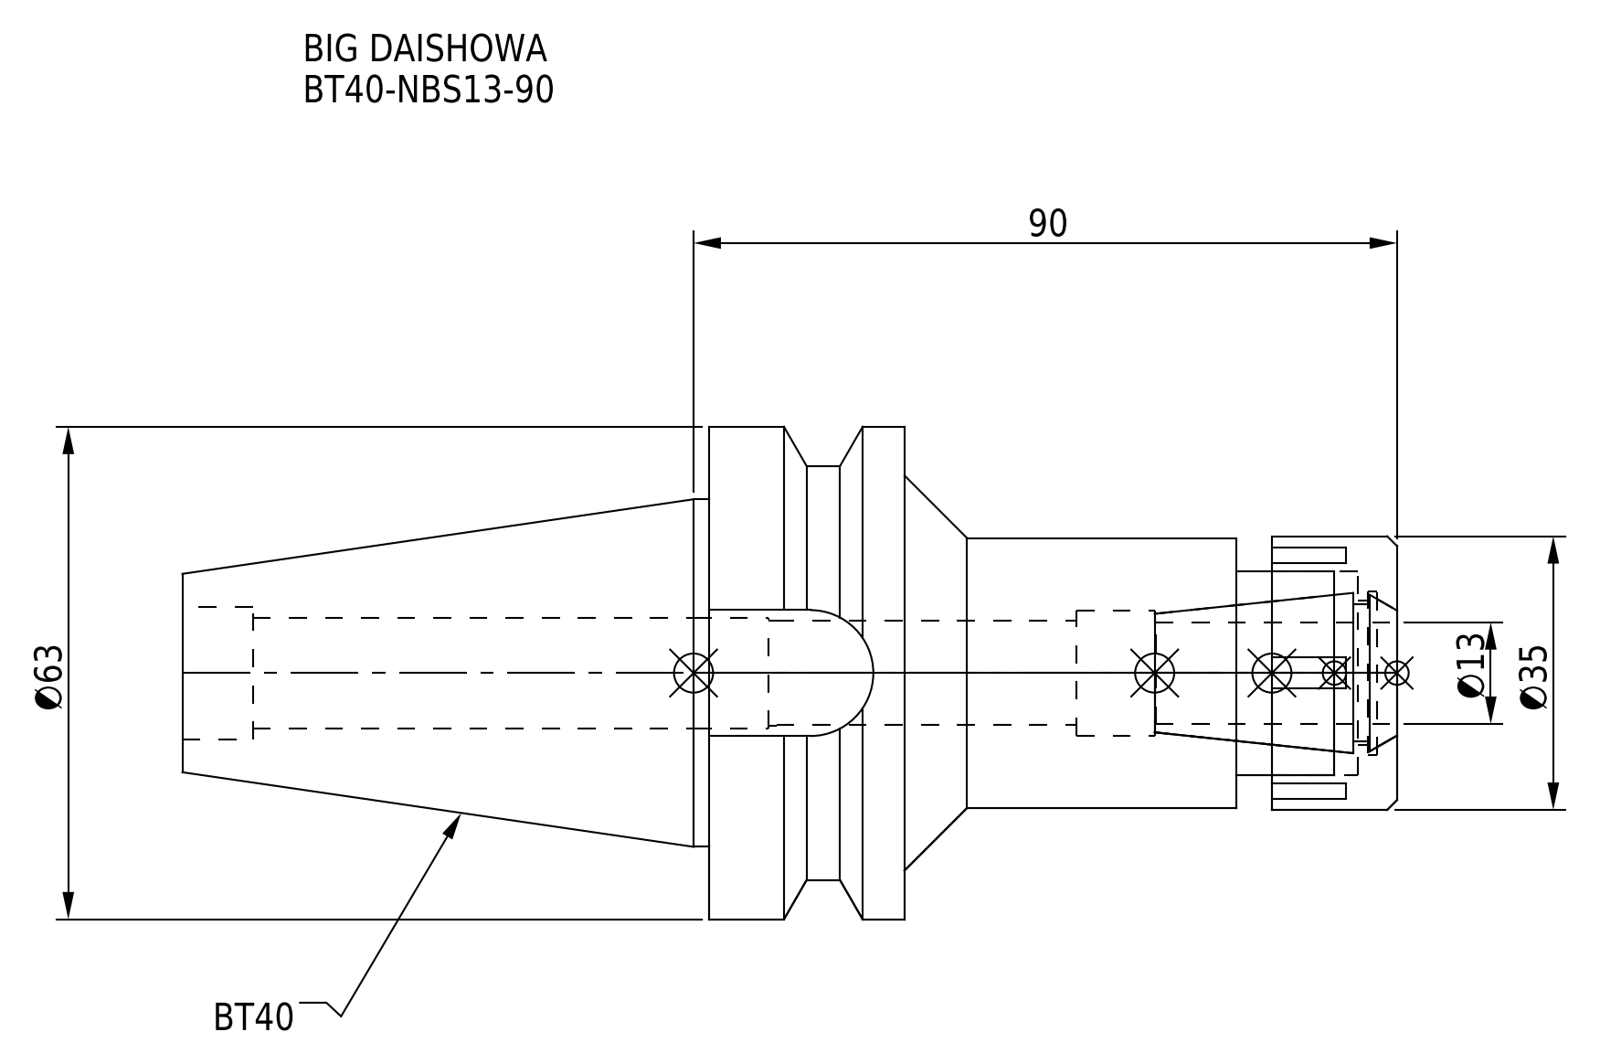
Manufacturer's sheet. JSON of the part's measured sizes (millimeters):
{"part_name": "NBN13_1.stp; DXF_TEMP_ASSY_ASM_4_ASM.stp; BT40NB13090-130_ASM.stp; BT40-NBS13-90.stp (+3 more)", "step_written_by": "SolidWorks 2019 (CONFIG_CONTROL_DESIGN)", "units": "millimeters", "bodies": {"solids": 2, "faces": 93, "planar": 45, "cylindrical": 34, "other": 14}, "overall_size": [155.4, 63, 63], "volume_mm3": 166605, "surface_area_mm2": 35164, "round_holes": [[13.3, 1], [13.5, 1], [14.2, 1], [16, 1], [17, 1], [18.5, 1], [21, 1], [26, 1]], "round_bosses_or_shafts": [[63, 1], [53, 1], [44.45, 1], [35, 1], [34.5, 1]], "partial_cylinders_radius": [[8.05, 1]], "face_to_face_distances": [25, 63, 88, 20.5, 47, 8, 42.5, 67.5, 16, 4.5]}
